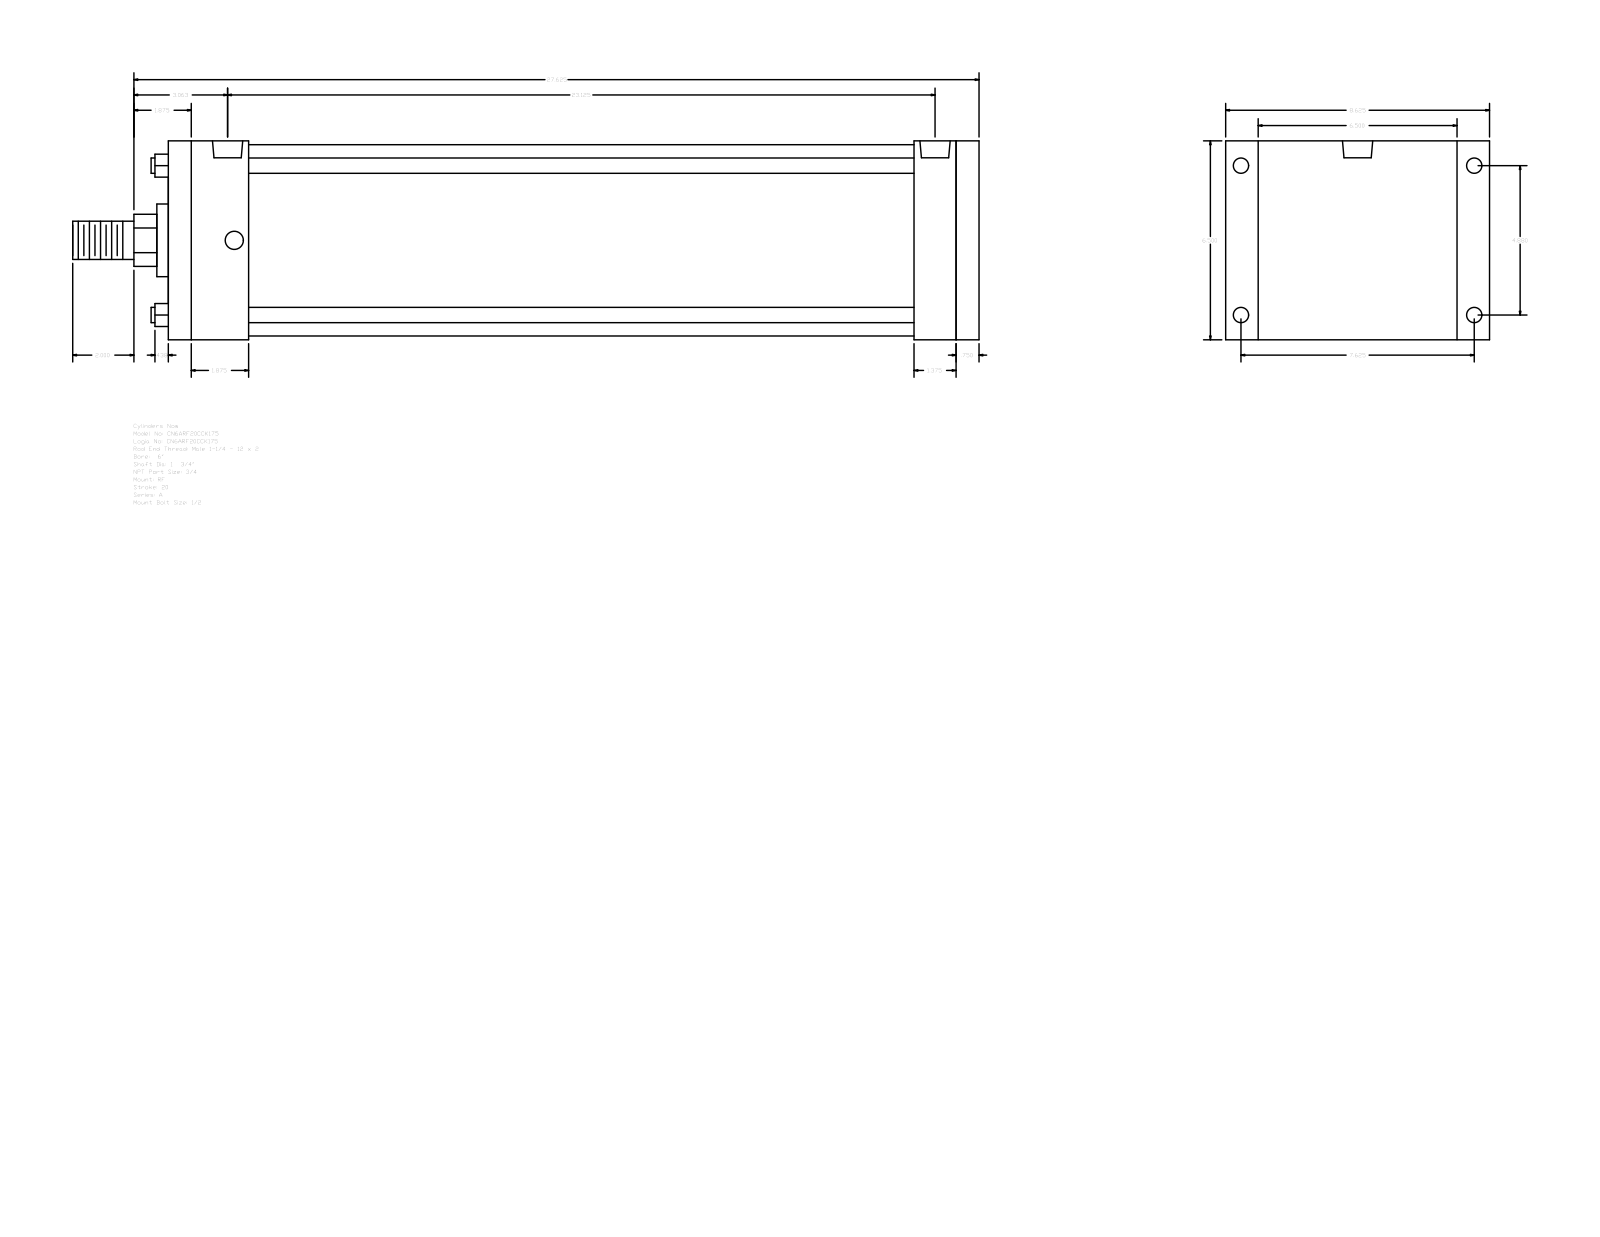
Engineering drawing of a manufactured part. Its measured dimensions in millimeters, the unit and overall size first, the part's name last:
Units: millimetres
Overall size (bounding box): 752.48 × 219.07 × 165.1
Round holes (diameter × count): ⌀12.7 ×4, ⌀15.08 ×4, ⌀25.12 ×2
Round bosses / shafts (diameter × count): ⌀12.7 ×4, ⌀158.75 ×1, ⌀60.33 ×1, ⌀44.45 ×1, ⌀31.75 ×1
Partial cylindrical surfaces — rounded edges, fillets, slot ends (radius × count): R21.63 ×1
Main face-to-face distances: 165.1, 673.1, 19.05, 654.05, 66.68, 587.37, 606.42, 619.13, 552.45, 34.92
Hole centre spacings: 5.56, 123.96, 193.68, 229.95, 576.25, 581.81, 587.37
Bodies: 0 solids, 92 faces (64 planar, 28 cylindrical, 0 other)
Part name (STEP PRODUCT): A_RF__0600_1.75
STEP written by: GSSL Pune (CONFIG_CONTROL_DESIGN)
